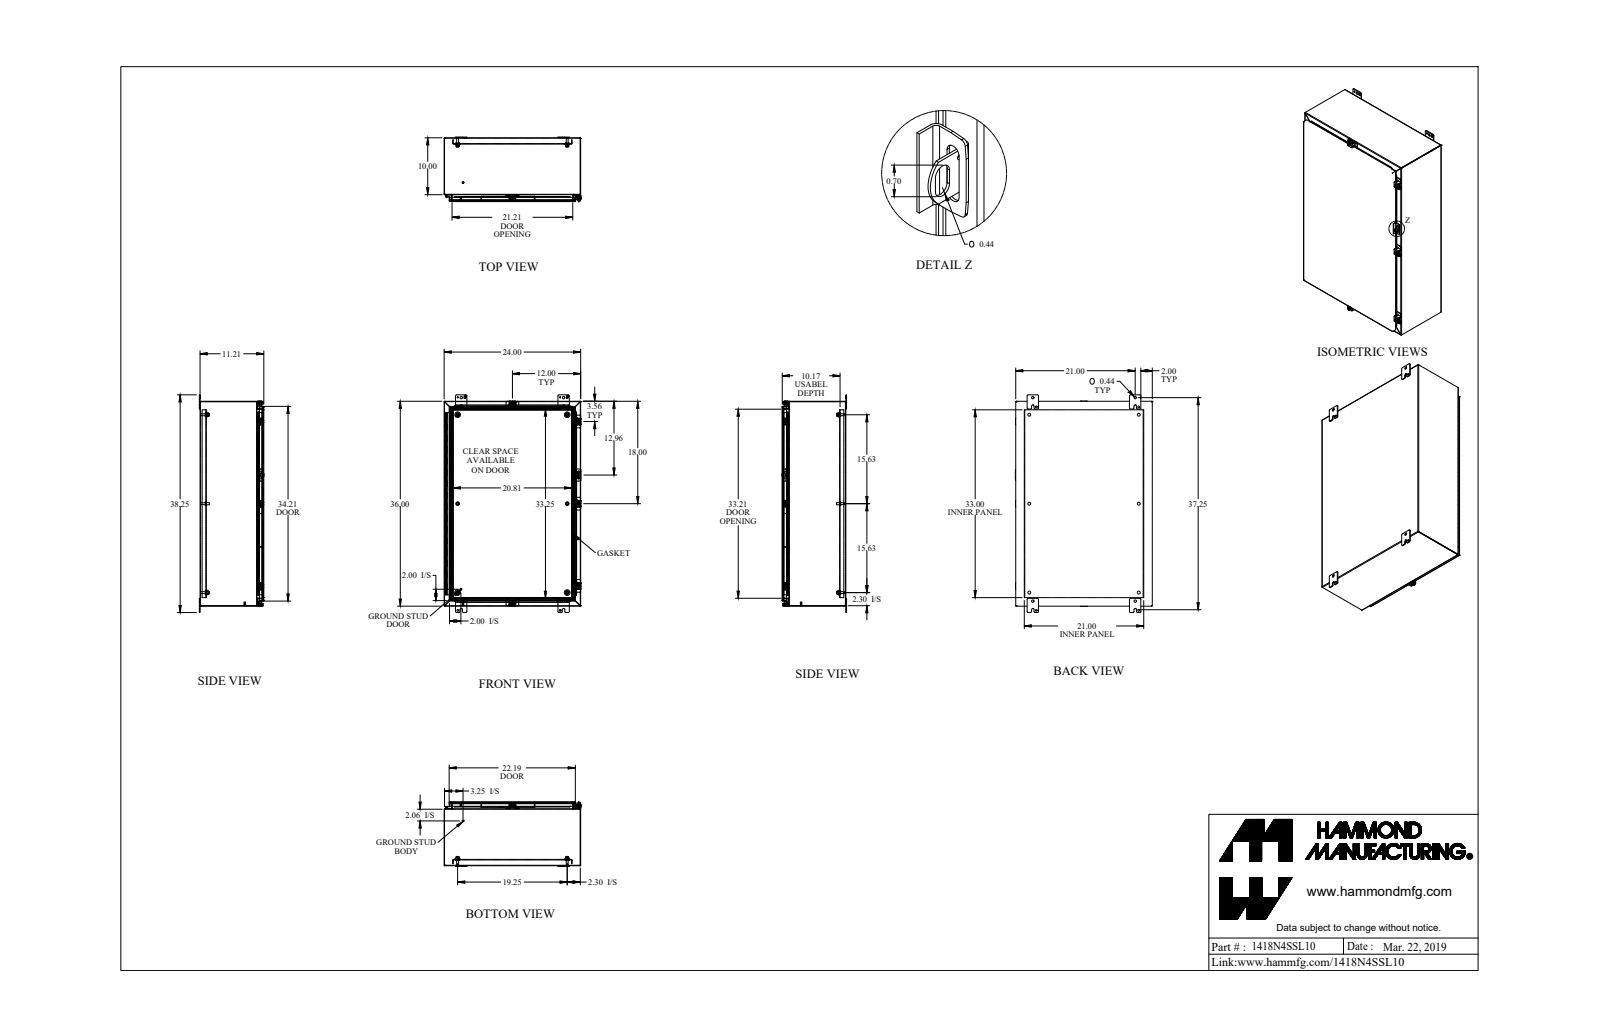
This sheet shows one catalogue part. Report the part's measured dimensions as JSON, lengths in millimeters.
{"part_name": "1418N4SSL10_Default", "step_written_by": "SolidWorks 2019 (CONFIG_CONTROL_DESIGN)", "units": "millimeters", "bodies": {"solids": 49, "faces": 1809, "planar": 1089, "cylindrical": 614, "other": 106}, "overall_size": [971.6, 611.2, 288.9], "volume_mm3": 5252000, "surface_area_mm2": 5430000, "round_holes": [[12.7, 6], [5.4, 5], [6.7, 5], [9.5, 5], [7.8, 4], [8, 4], [11.1, 4], [11.3, 4], [3.2, 1], [4.7, 1]], "round_bosses_or_shafts": [[16.5, 6], [9.5, 6], [8.4, 6], [12.7, 5], [9.9, 5], [6.2, 5], [25.4, 4], [8, 2]], "partial_cylinders_radius": [[1.2, 27], [3.6, 27], [4.8, 26], [0.9, 24], [2.7, 24], [6.4, 24], [3.2, 10], [3.6, 10]], "face_to_face_distances": [1.8, 281.1, 282.9, 1.8, 282.9, 284.7, 2.4, 23.8, 25.6, 607.8], "hole_center_spacings": [396.9, 882.3, 489, 793.8, 250.4, 932.3, 250.4, 457.2]}
